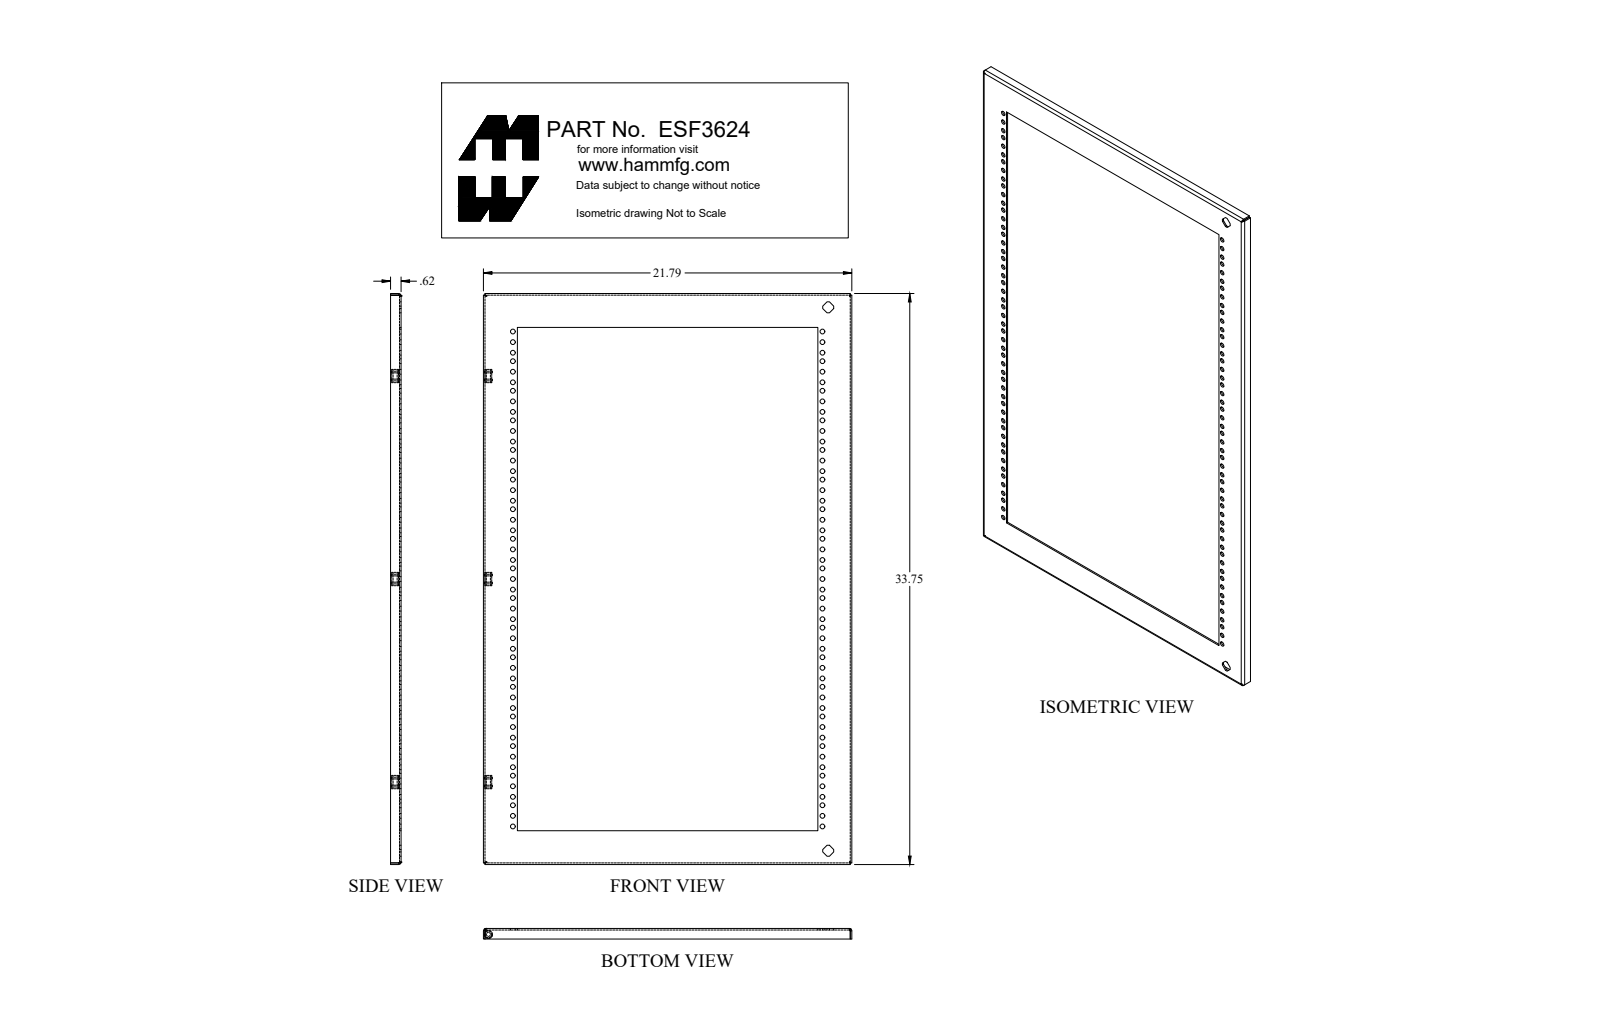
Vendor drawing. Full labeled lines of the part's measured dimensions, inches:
Part name (STEP PRODUCT): ESF3624
STEP written by: SolidWorks 2018 (AUTOMOTIVE_DESIGN)
Units: inches
Bodies: 20 solids, 870 faces (400 planar, 400 cylindrical, 70 other)
Overall size (bounding box): 33.75 × 23.706 × 6.372
Volume: 44.02 in³ · Surface area: 1 153 in²
Round holes (diameter × count): ⌀0.281 ×102, ⌀0.136 ×3, ⌀0.19 ×3, ⌀0.242 ×3, ⌀0.516 ×2
Round bosses / shafts (diameter × count): ⌀0.356 ×3, ⌀0.278 ×3, ⌀0.226 ×3, ⌀0.788 ×2, ⌀0.535 ×2, ⌀0.496 ×2, ⌀0.435 ×2
Partial cylindrical surfaces — rounded edges, fillets, slot ends (radius × count): R0.048 ×28, R0.01 ×24, R0.036 ×6, R0.108 ×6, R0.06 ×4, R0.143 ×4, R0.153 ×4, R0.156 ×4
Main face-to-face distances: 0.095, 0.072, 22.008, 22.08, 0.78, 0.875, 0.852, 0.947, 21.936, 0.038
Hole centre spacings: 1.75, 3.5, 5.25, 7, 8.75, 10.5, 0.625, 0.625
